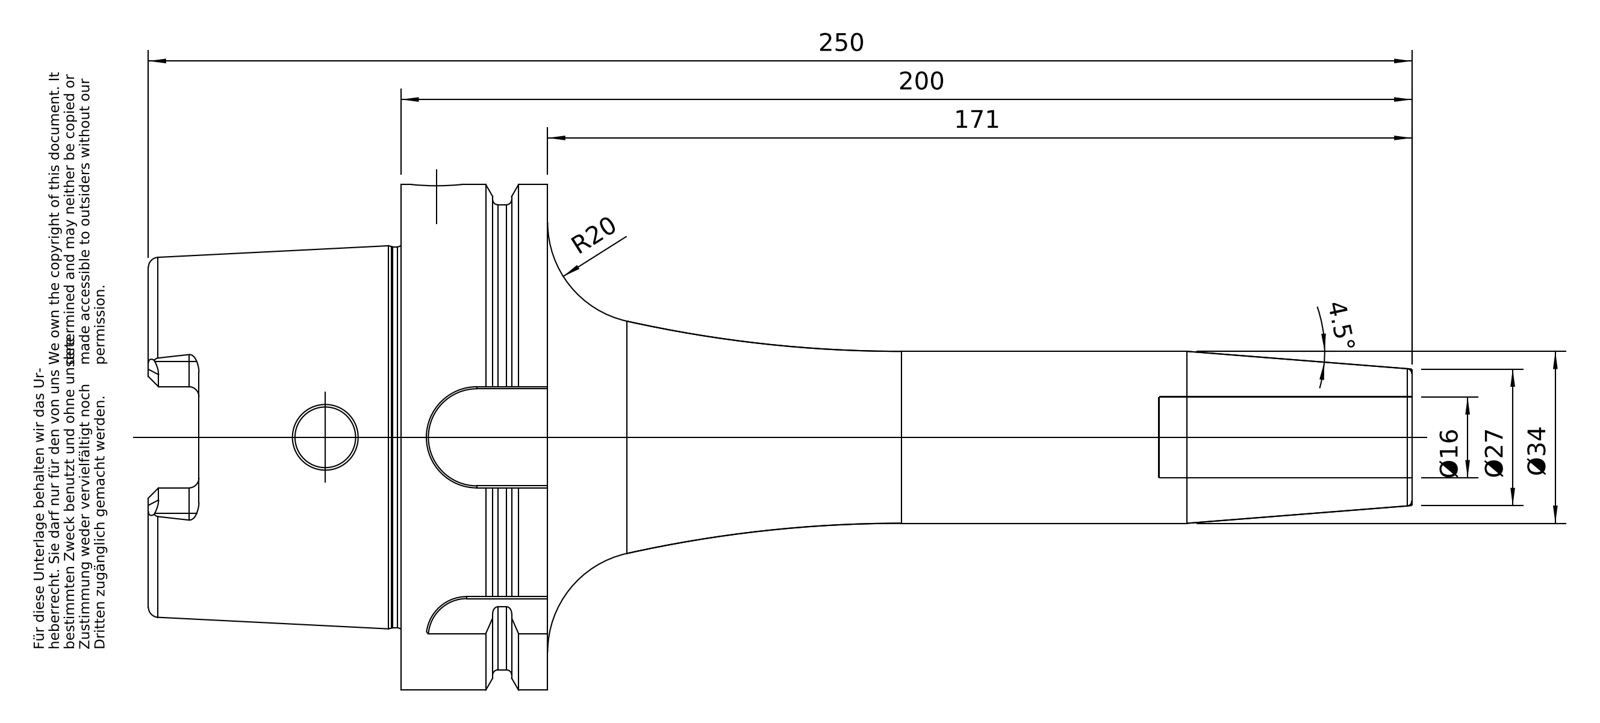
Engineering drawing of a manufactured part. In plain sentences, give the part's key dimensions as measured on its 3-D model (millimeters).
The part is named "A100-146-16". Its 3-D file was written by "PRO/ENGINEER BY PARAMETRIC TECHNOLOGY CORPORATION, 2010430 (CONFIG_CONTROL_DESIGN)". It is 1 solid with 176 faces: 50 planar, 51 cylindrical and 75 other. Overall it measures 250 by 100 by 100 millimeters. Its volume is 429 511 cubic millimeters and its surface area 69 720 square millimeters. Round holes: 1 of diameter 10, 1 of diameter 12, 1 of diameter 16, 1 of diameter 22.5, 1 of diameter 24, 1 of diameter 24.32, 1 of diameter 24.5, 1 of diameter 53, 1 of diameter 63. Round bosses or shafts: 1 of diameter 100, 1 of diameter 92, 1 of diameter 75.36, 1 of diameter 34. Partial cylindrical surfaces (rounded edges, fillets, slot ends): 6 of radius 2, 4 of radius 5, 1 of radius 8, 1 of radius 10, 1 of radius 11. The main face-to-face distances are 29, 12.5, 16.5, 50, 62.5, 79, 200, 88, 78.5, 28.5.
